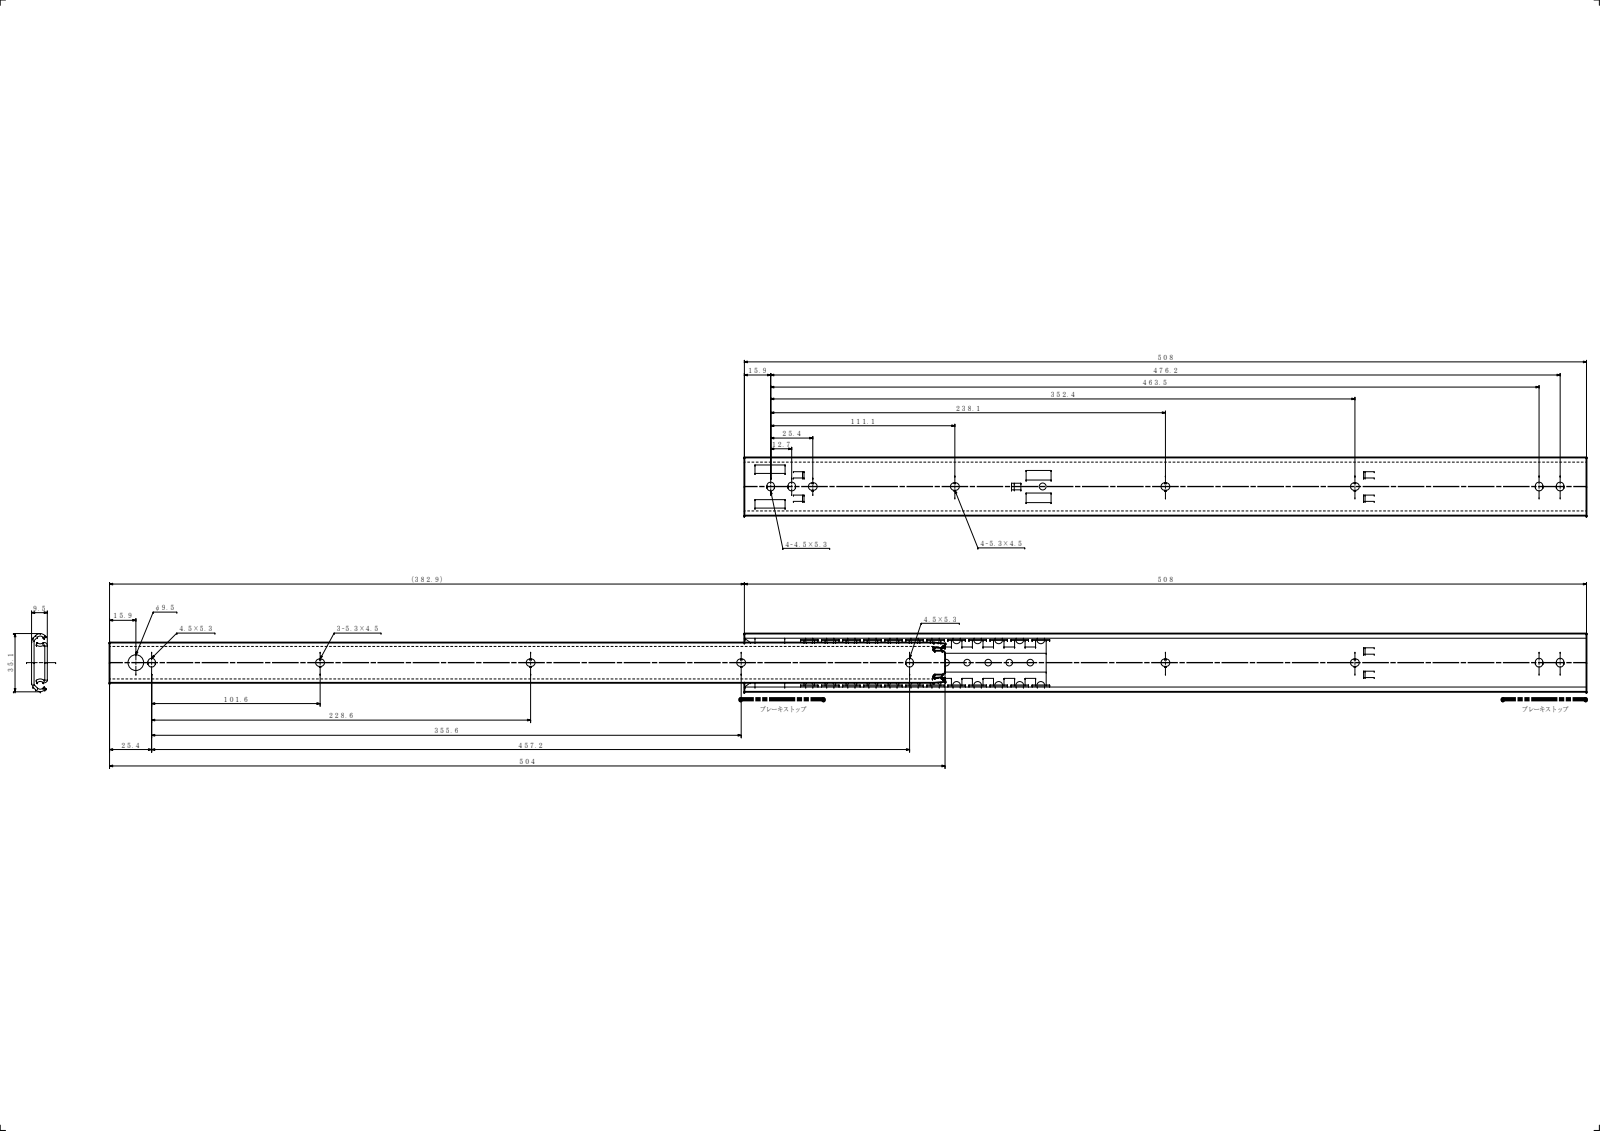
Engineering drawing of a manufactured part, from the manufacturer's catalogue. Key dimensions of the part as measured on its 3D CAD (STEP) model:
Part name (STEP PRODUCT): PN84 ol; U22-20; IM U22-20; PN101リベット (+2 more)
STEP written by: SolidWorks 2019 (CONFIG_CONTROL_DESIGN)
Units: millimetres
Bodies: 5 solids, 294 faces (155 planar, 135 cylindrical, 4 other)
Overall size (bounding box): 890.9 × 35.1 × 9.5
Volume: 60 599 mm³ · Surface area: 85 065 mm²
Round holes (diameter × count): ⌀2.4 ×1, ⌀2.6 ×1, ⌀4.2 ×1, ⌀9.5 ×1
Round bosses / shafts (diameter × count): ⌀4.6 ×2, ⌀2.3 ×1
Partial cylindrical surfaces — rounded edges, fillets, slot ends (radius × count): R2.25 ×30, R0.3 ×12, R0.4 ×8, R0.5 ×6, R0.8 ×6, R3 ×6, R0.1 ×4, R2 ×4
Main face-to-face distances: 1.5, 8, 9.5, 6.5, 25.59, 4.88, 3.38, 24.09, 20.71, 27.09
Hole centre spacings: 547
